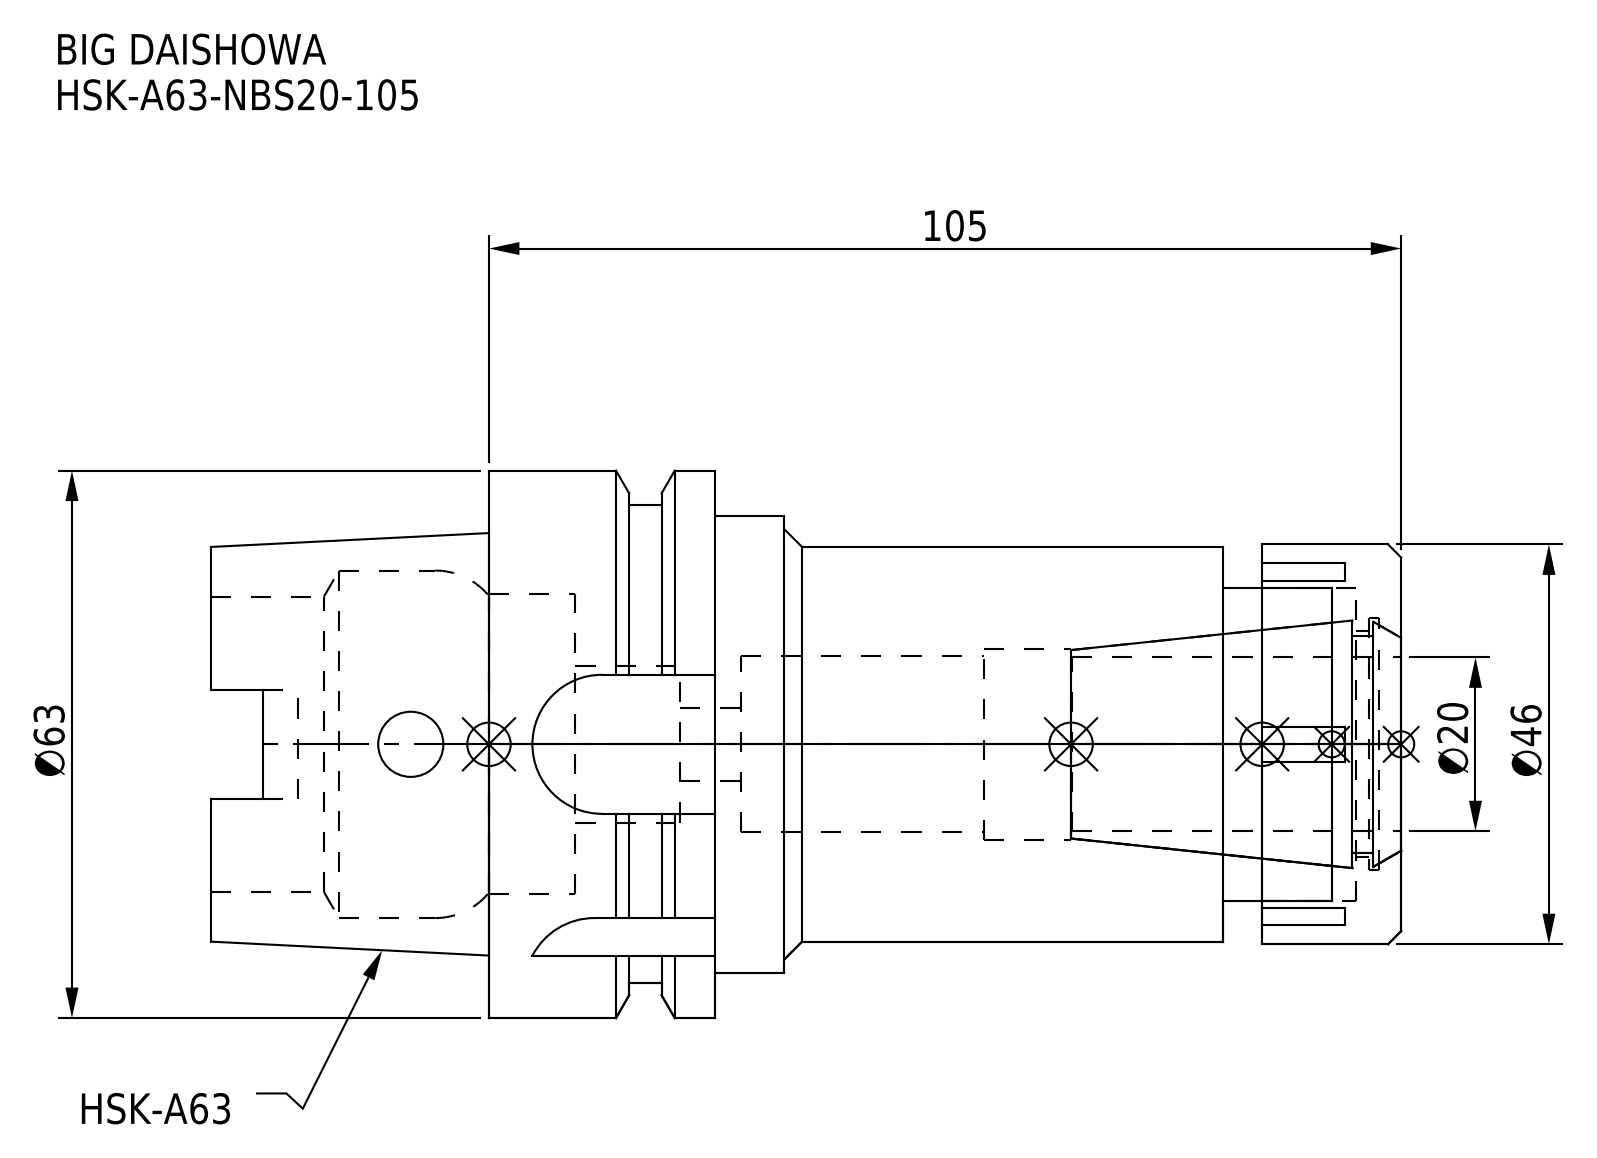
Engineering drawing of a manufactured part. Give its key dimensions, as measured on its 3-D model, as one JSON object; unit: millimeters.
{"part_name": "NBN20_1.stp; DXF_TEMP_ASSY_ASM_4_ASM.stp; HSK-A63-NBS20-105_1.stp; HA63NB20105-200_ASM.stp (+3 more)", "step_written_by": "SolidWorks 2019 (CONFIG_CONTROL_DESIGN)", "units": "millimeters", "bodies": {"solids": 2, "faces": 141, "planar": 70, "cylindrical": 49, "other": 22}, "overall_size": [137, 63, 63], "volume_mm3": 178325, "surface_area_mm2": 43520, "round_holes": [[7.5, 1], [8.4, 1], [18, 1], [20.3, 1], [22, 1], [26, 1], [29, 1], [34, 1], [34.5, 1], [36, 1], [40, 1]], "round_bosses_or_shafts": [[63, 1], [55, 1], [52.6, 1], [46, 1], [45.5, 1]], "partial_cylinders_radius": [[2.88, 4], [8, 4]], "face_to_face_distances": [8, 105, 26, 79, 63, 95.05, 16.05, 9.95, 71, 89]}
